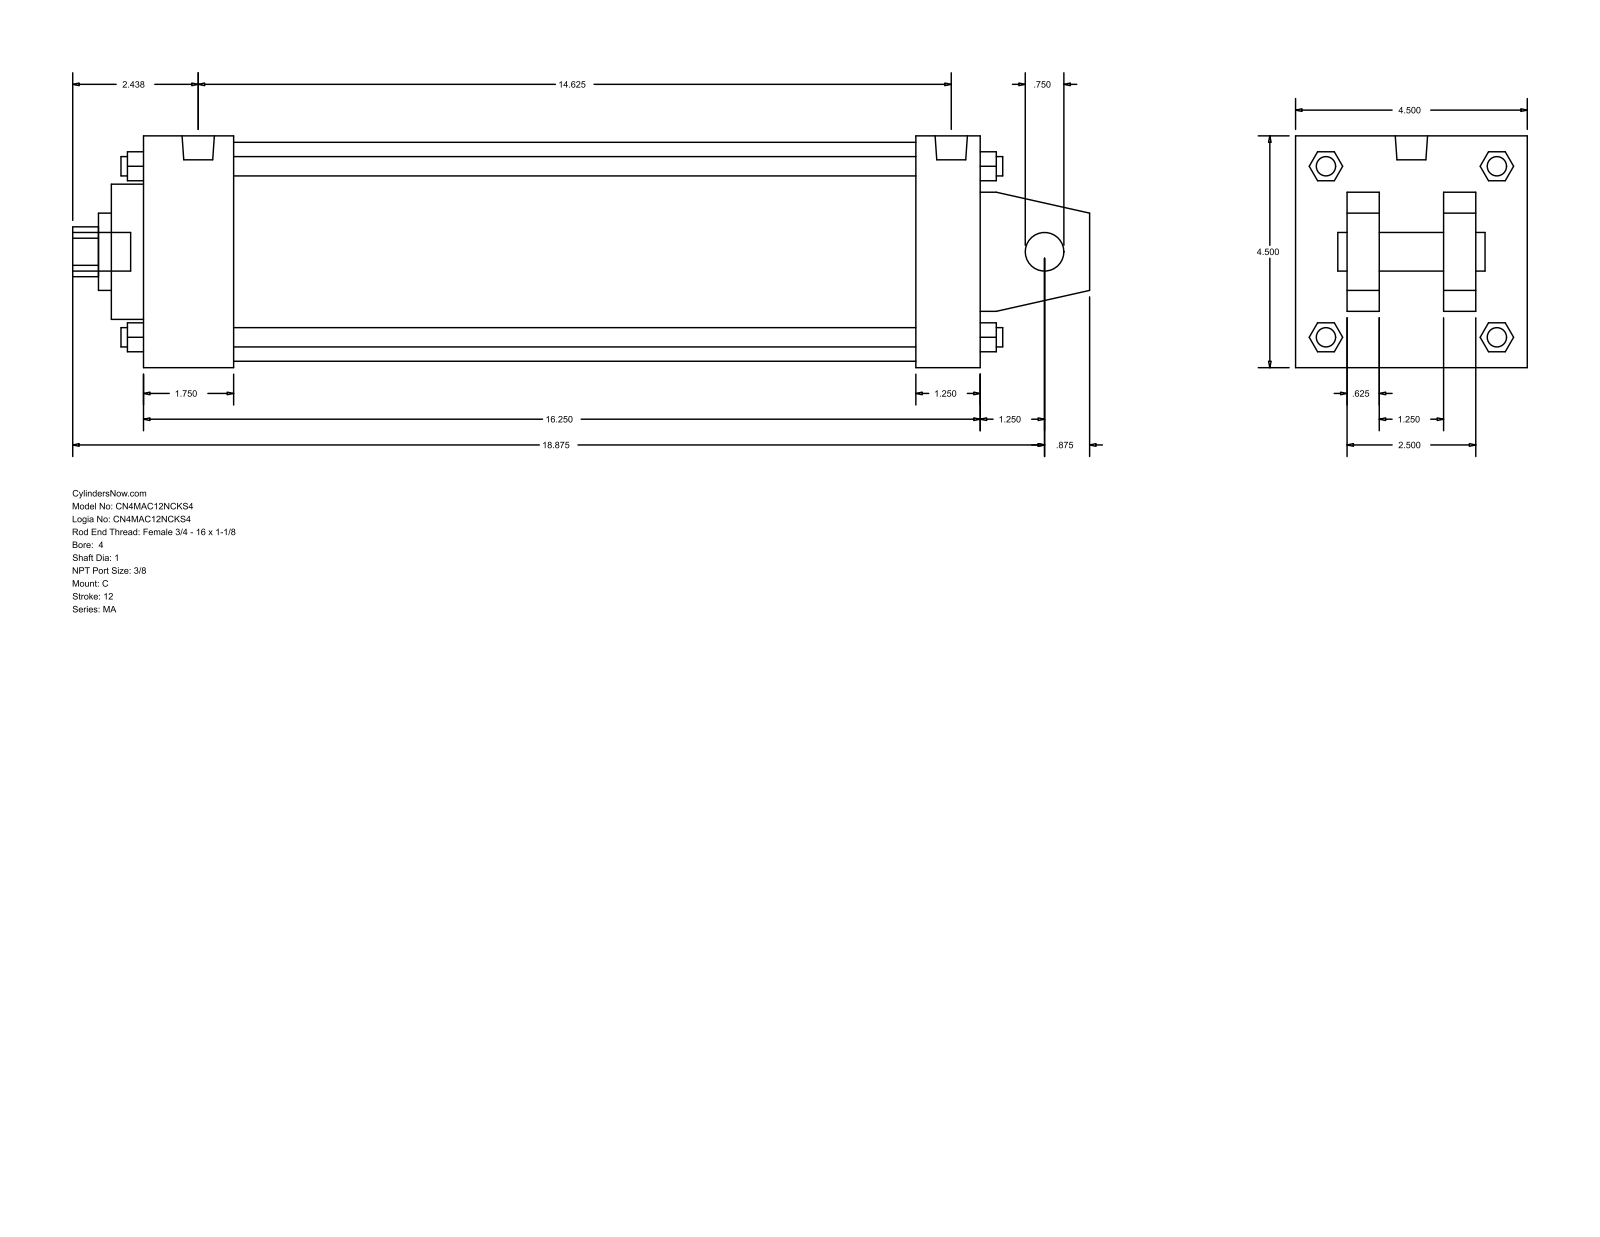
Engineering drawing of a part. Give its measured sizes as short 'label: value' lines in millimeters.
name: MA_C__0400_1
written by: GSSL Pune (CONFIG_CONTROL_DESIGN)
unit: mm
bodies: 0 solids, 141 faces (109 planar, 32 cylindrical, 0 other)
size: 501.65 × 114.3 × 114.3
holes: 1× ⌀19.05, 1× ⌀25.4, 1× ⌀38.1, 1× ⌀66.67, 1× ⌀107.95
bosses: 4× ⌀11.11, 4× ⌀9.53, 2× ⌀15.93, 1× ⌀19.05
rounds: 1× R12.29
face distances: 114.3, 412.76, 15.87, 73.03, 41.27, 25.4, 88.9, 47.63, 381.01, 31.75
